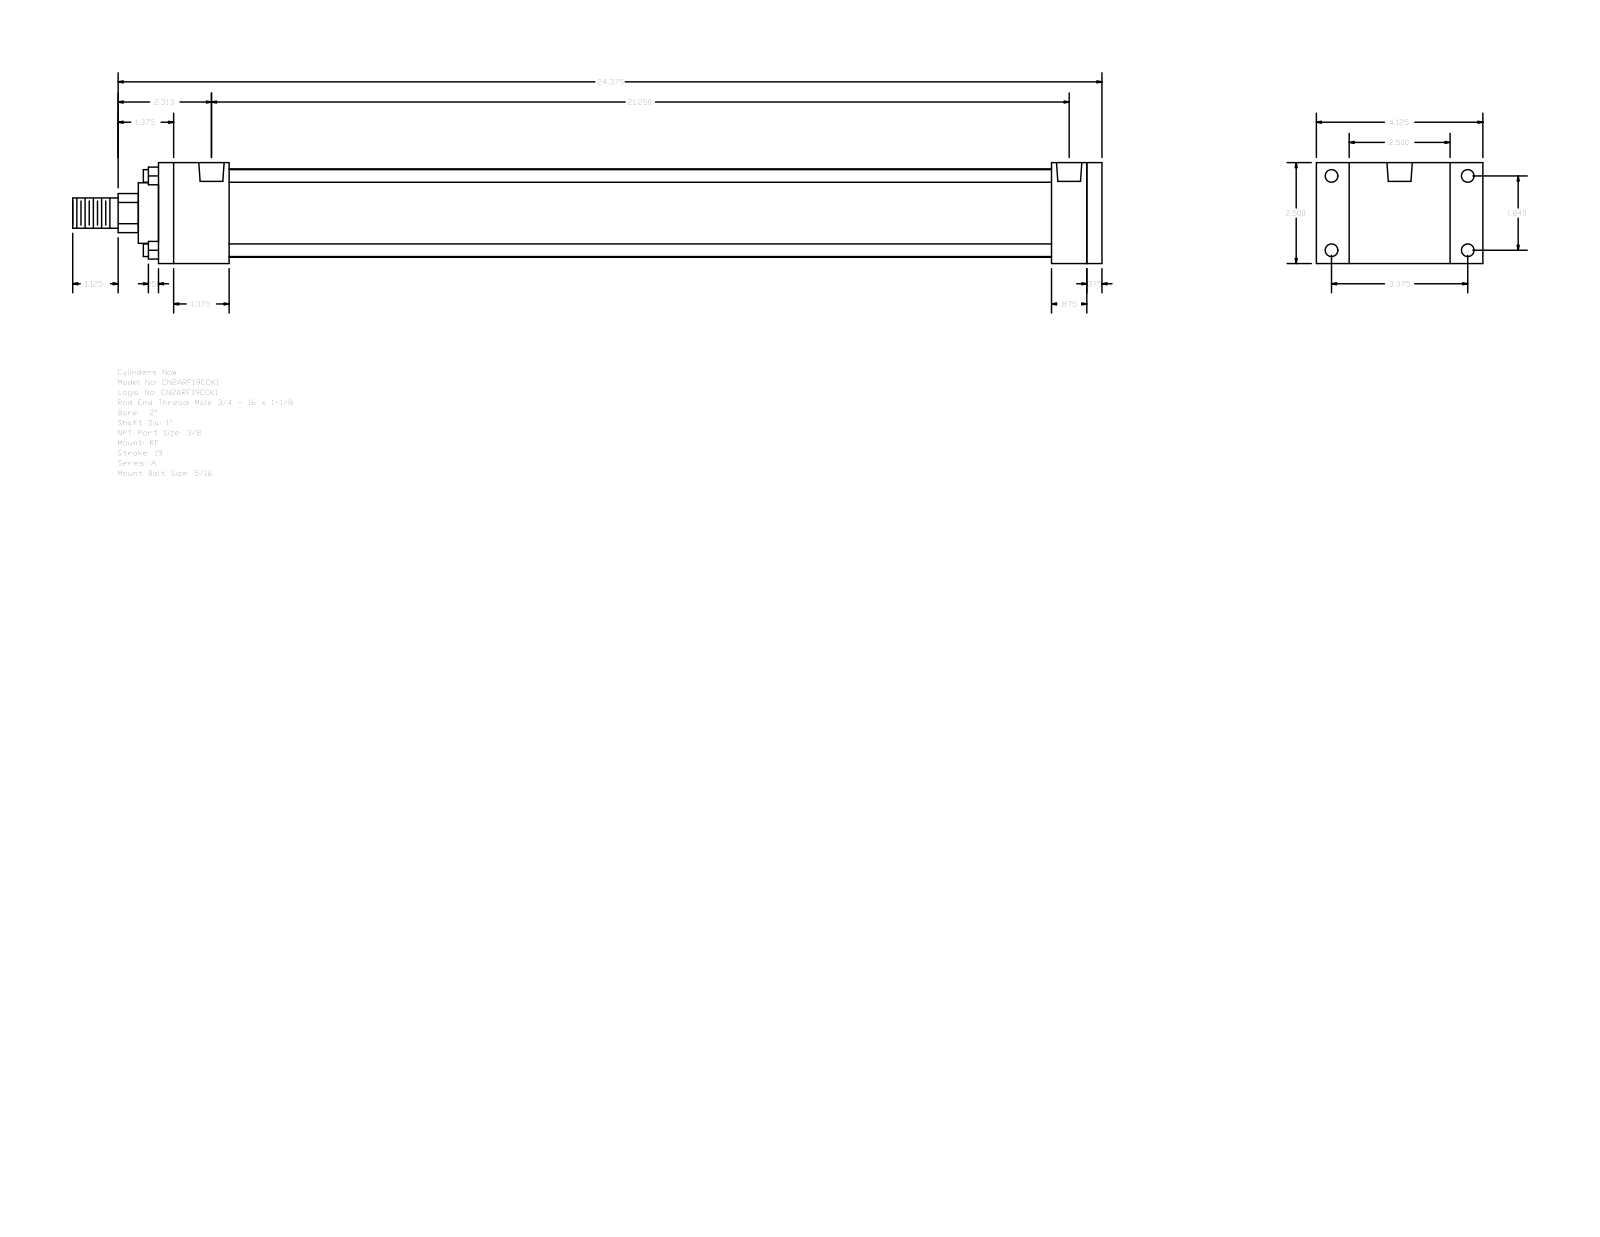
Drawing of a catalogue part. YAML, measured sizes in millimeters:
part_name: "A_RF__0200_1"
step_written_by: "GSSL Pune (CONFIG_CONTROL_DESIGN)"
units: millimeters
bodies: {solids: 0, faces: 92, planar: 64, cylindrical: 28, other: 0}
overall_size: [647.7, 104.78, 63.5]
round_holes:
  - {diameter: 5.56, count: 4}
  - {diameter: 7.94, count: 4}
  - {diameter: 15.93, count: 2}
round_bosses_or_shafts:
  - {diameter: 7.94, count: 4}
  - {diameter: 55.63, count: 1}
  - {diameter: 38.1, count: 1}
  - {diameter: 25.4, count: 1}
  - {diameter: 19.05, count: 1}
partial_cylinders:
  - {radius: 12.29, count: 1}
face_to_face_distances: [63.5, 9.52, 593.72, 584.2, 44.45, 20.64, 539.75, 549.27, 561.98, 517.53]
hole_center_spacings: [46.74, 85.72, 97.63, 534.18, 1.59, 3.98, 535.77, 538.16]
